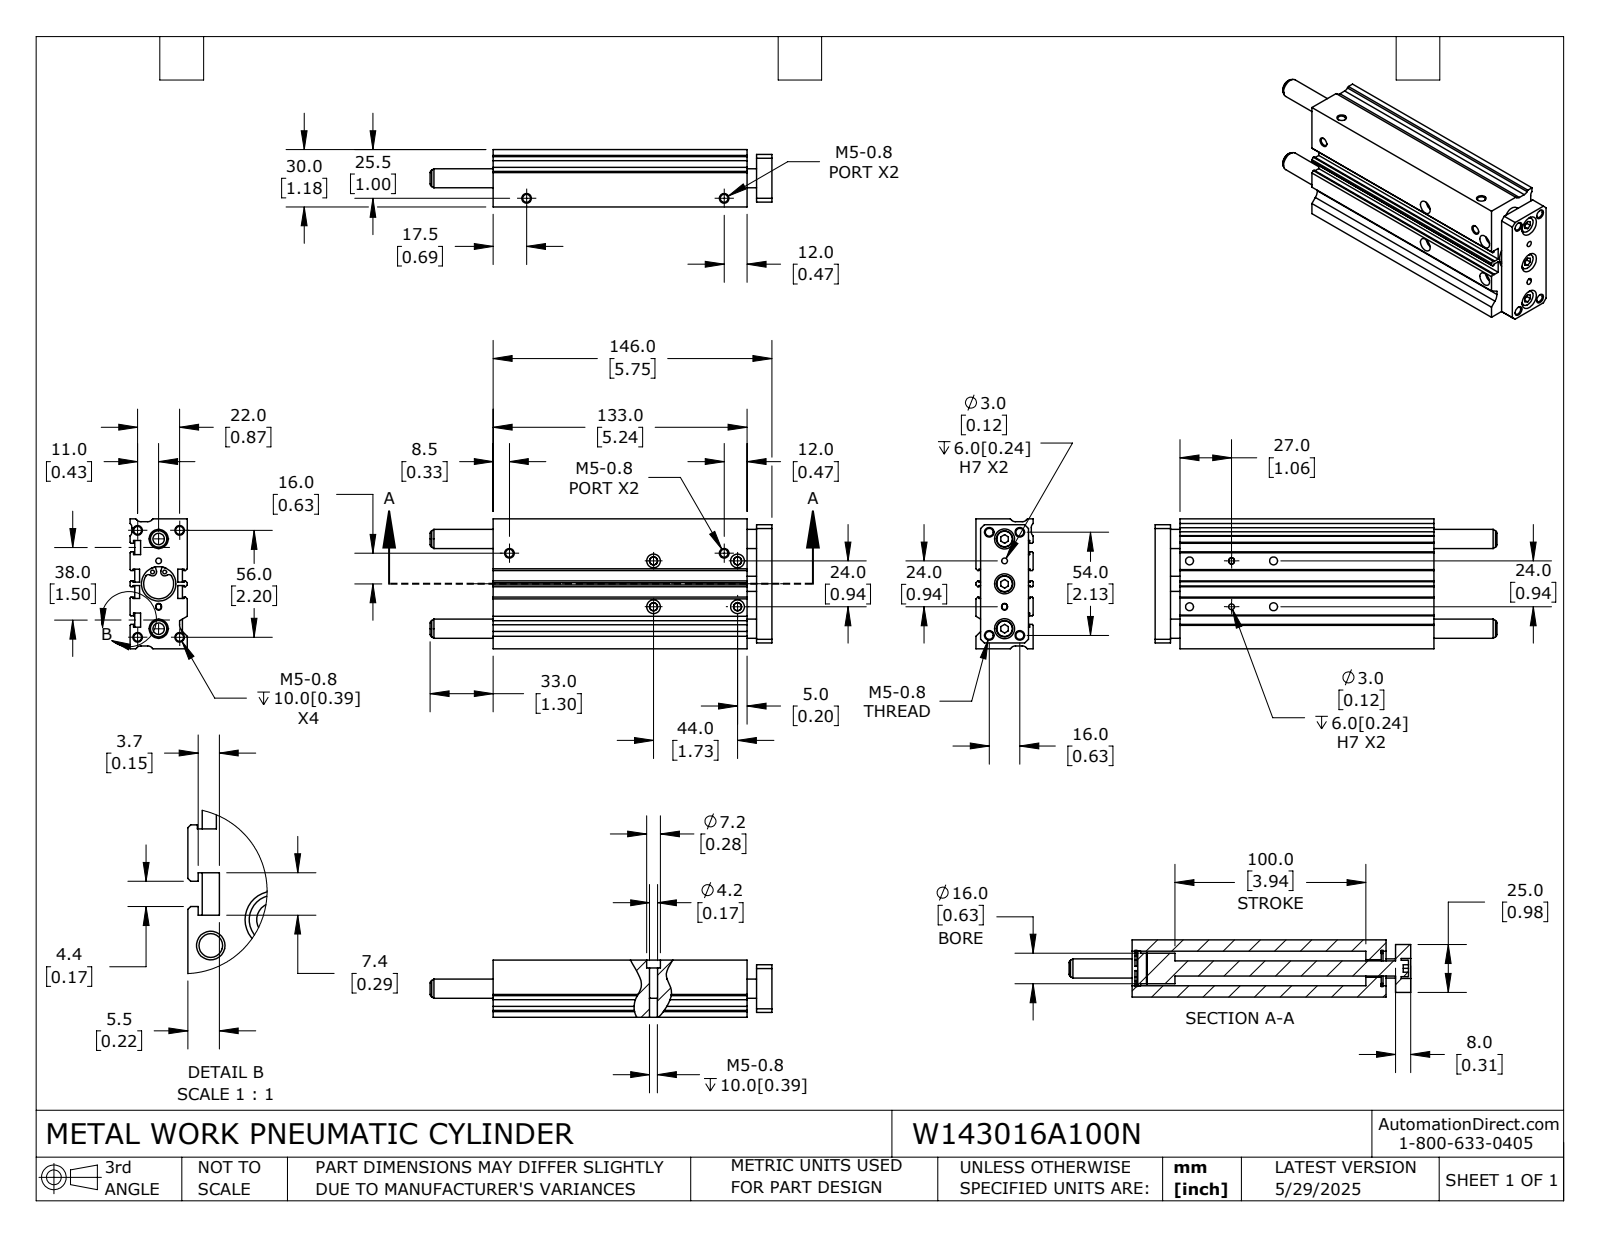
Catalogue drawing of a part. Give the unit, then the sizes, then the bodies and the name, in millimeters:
Units: millimetres
Overall size (bounding box): 179 × 68 × 30
Round holes (diameter × count): ⌀4.13 ×16, ⌀2 ×4, ⌀3 ×4, ⌀4.2 ×4, ⌀7.2 ×4, ⌀10.5 ×3, ⌀10 ×2, ⌀9.2 ×1, ⌀15.7 ×1, ⌀18 ×1
Round bosses / shafts (diameter × count): ⌀8.5 ×3, ⌀19 ×2, ⌀16 ×1, ⌀8 ×1
Partial cylindrical surfaces — rounded edges, fillets, slot ends (radius × count): R3 ×6, R1.5 ×4, R1.58 ×4, R2.07 ×4, R5 ×1
Main face-to-face distances: 5, 30, 25, 68, 1.5, 2.5, 0.5, 5.5, 33.15, 24.5
Hole centre spacings: 22, 3.16, 6.62, 6.95, 8.73, 11.88, 17, 17.6
Volume: 228 827 mm³ · Surface area: 80 938 mm²
Bodies: 5 solids, 344 faces (169 planar, 137 cylindrical, 38 other)
Part name (STEP PRODUCT): W143016A100N; W143016A100N_ROD; W143016A100N_BODY
STEP written by: SolidWorks 2024 (CONFIG_CONTROL_DESIGN)
